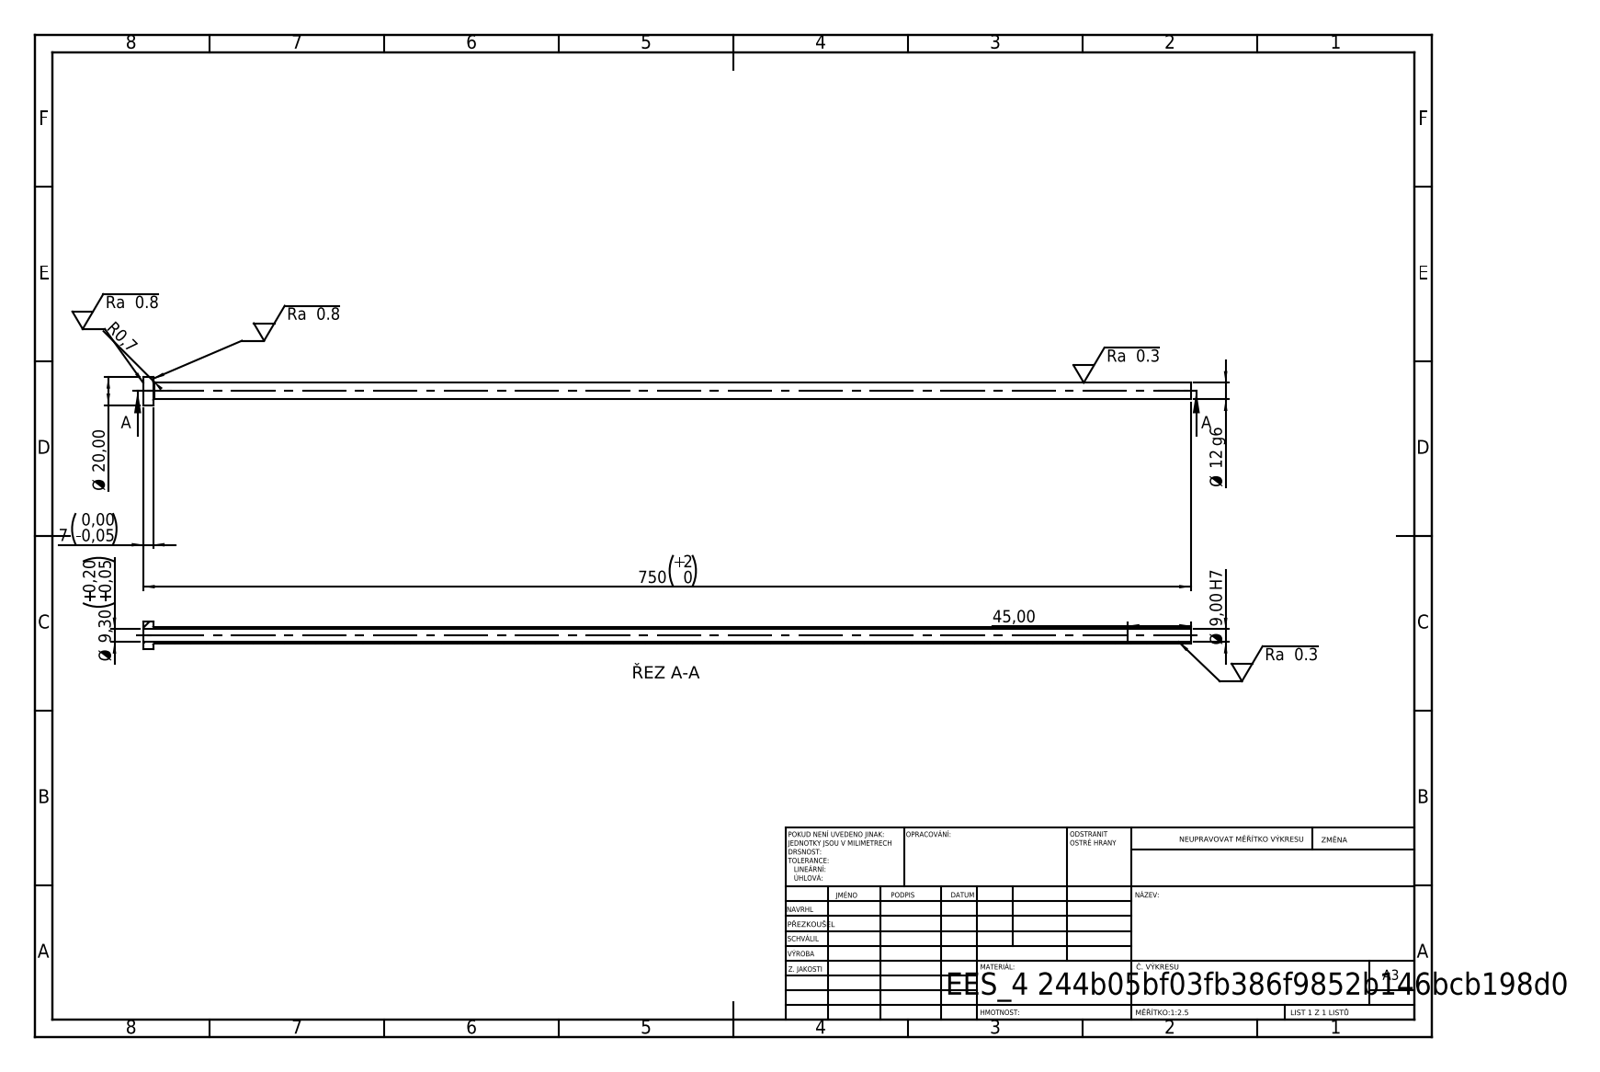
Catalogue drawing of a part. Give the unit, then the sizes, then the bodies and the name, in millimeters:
Units: millimetres
Overall size (bounding box): 750 × 20 × 20
Round holes (diameter × count): ⌀9 ×1, ⌀9.3 ×1
Round bosses / shafts (diameter × count): ⌀20 ×1, ⌀12 ×1
Main face-to-face distances: 7, 750, 743, 705, 698, 45
Volume: 35 482 mm³ · Surface area: 50 810 mm²
Bodies: 1 solid, 14 faces (4 planar, 8 cylindrical, 2 other)
STEP written by: SolidWorks 2019 (CONFIG_CONTROL_DESIGN)
